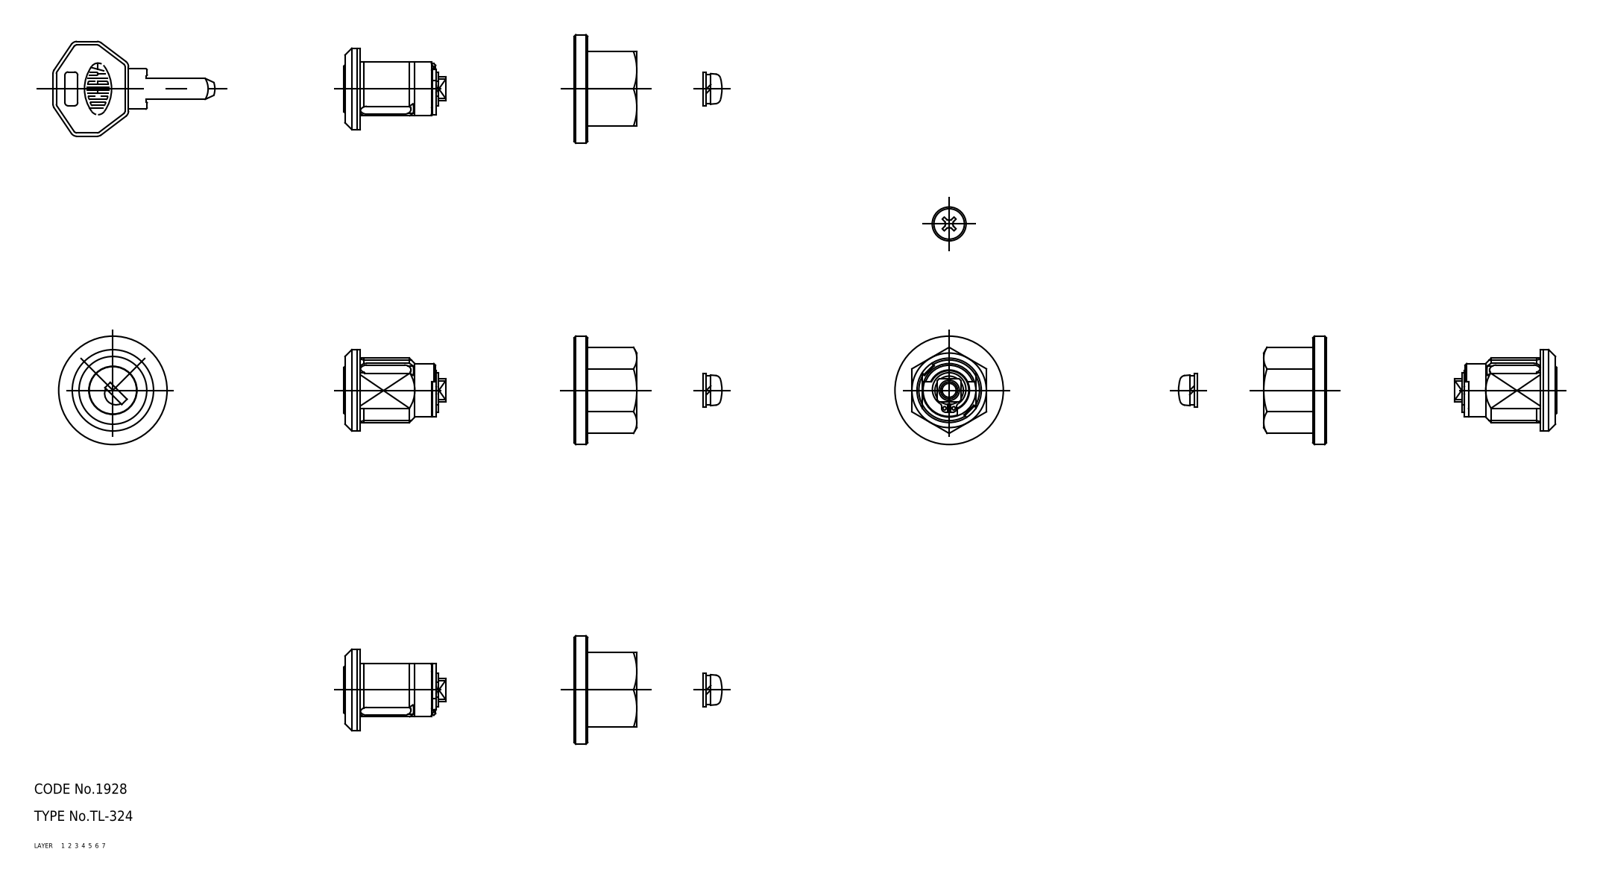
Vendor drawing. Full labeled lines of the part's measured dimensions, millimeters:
Part name (STEP PRODUCT): screw; retainer; packing; nut (+4 more)
STEP written by: CADfix (AUTOMOTIVE_DESIGN)
Units: millimetres
Bodies: 8 solids, 278 faces (0 planar, 0 cylindrical, 278 other)
Overall size (bounding box): 126.47 × 32 × 32
Volume: 12 732 mm³ · Surface area: 10 164 mm²
